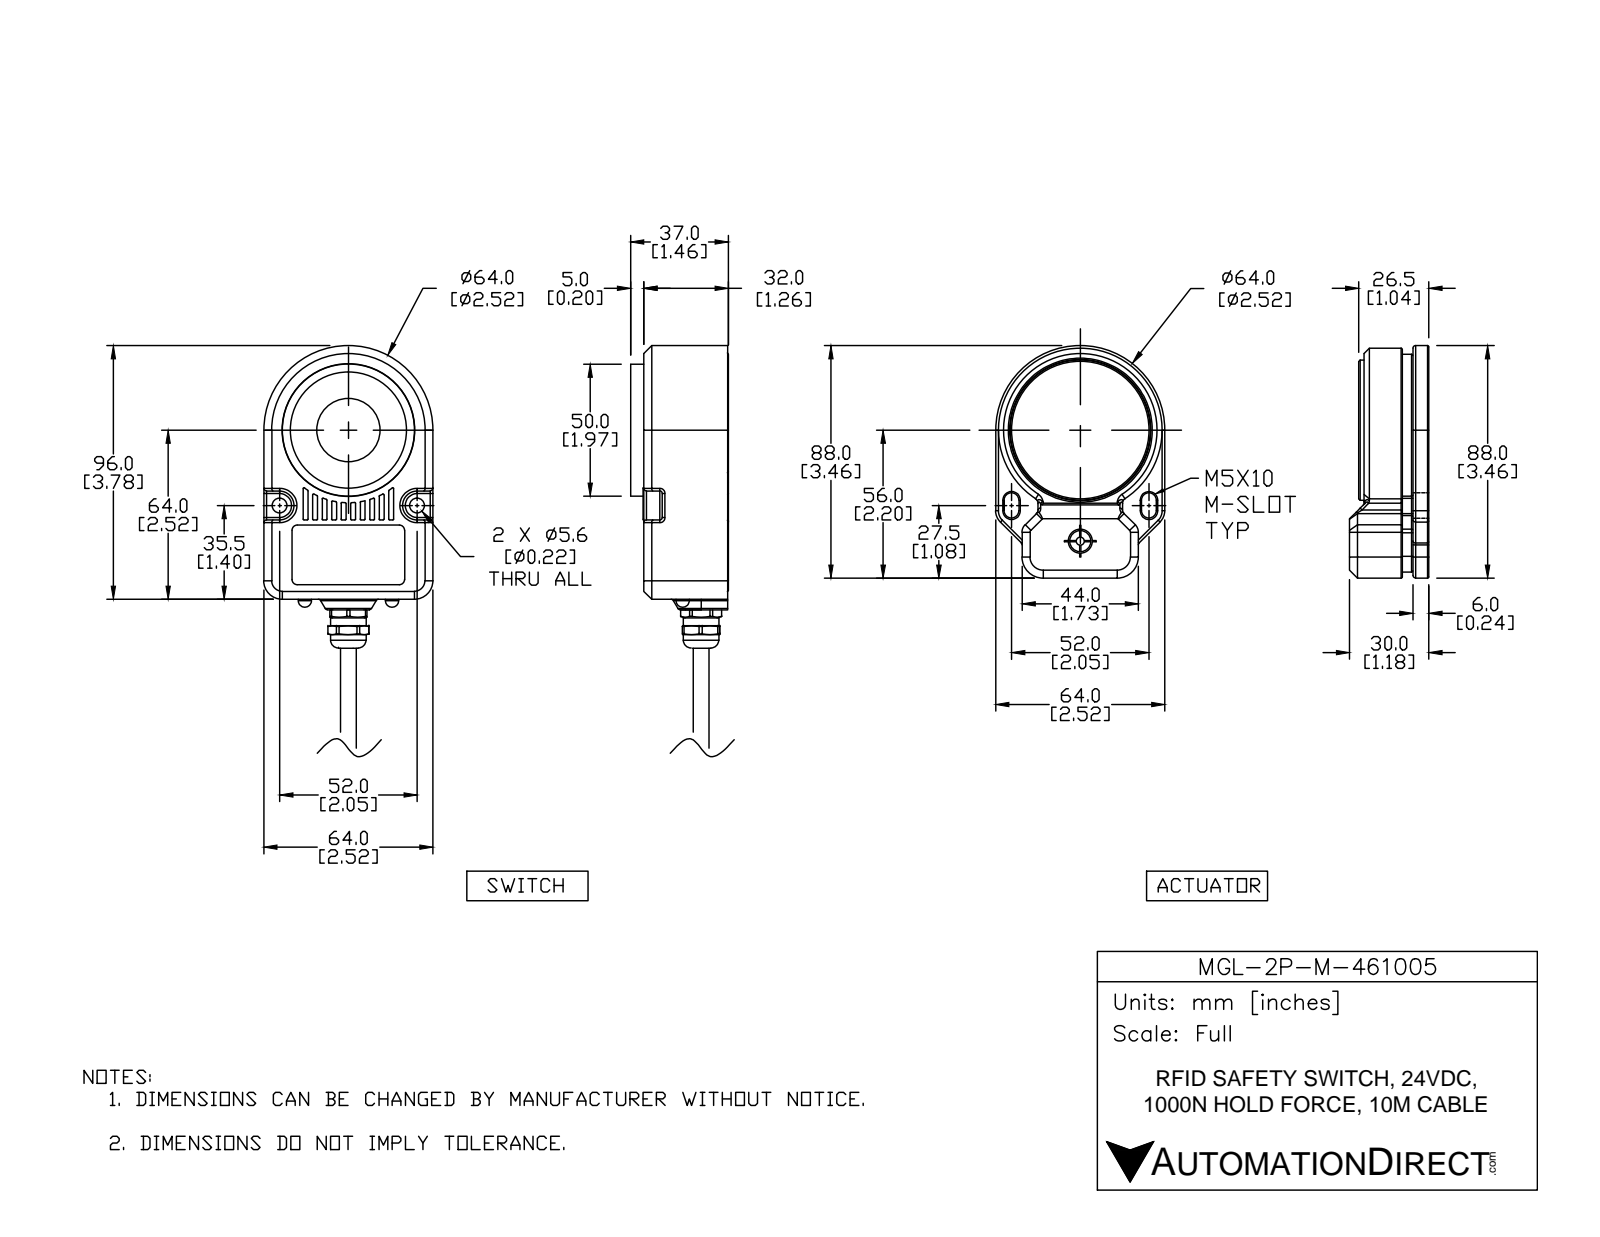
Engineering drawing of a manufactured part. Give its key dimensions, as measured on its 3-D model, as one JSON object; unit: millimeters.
{"part_name": "MGL-2P-M-461005_1; MGL-2P-M-461005; MGL-2P-M-461005_2", "step_written_by": "SolidWorks 2017 (AUTOMOTIVE_DESIGN)", "units": "millimeters", "bodies": {"solids": 17, "faces": 1585, "planar": 431, "cylindrical": 674, "other": 480}, "overall_size": [196, 64.5, 64], "volume_mm3": 194400, "surface_area_mm2": 99680, "round_holes": [[4, 6], [8, 6], [2.4, 4], [5, 4], [2, 2], [3.3, 2], [5.6, 2], [9, 2], [10.5, 2], [17, 2], [6.4, 1], [6.5, 1]], "round_bosses_or_shafts": [[0.5, 4], [2, 3], [12, 2], [6, 2], [5.8, 2], [5.4, 2], [3.7, 2], [62, 1]], "partial_cylinders_radius": [[0.5, 180], [1, 60], [0.3, 39], [2, 20], [0.6, 7], [4, 6], [6, 5], [8, 5]], "face_to_face_distances": [2.5, 6, 58.5, 10.5, 16.5, 64.5, 3, 61.5, 10, 8], "hole_center_spacings": [17.9, 19.5, 27.6, 17, 26, 29.4, 4.4, 8.8]}
